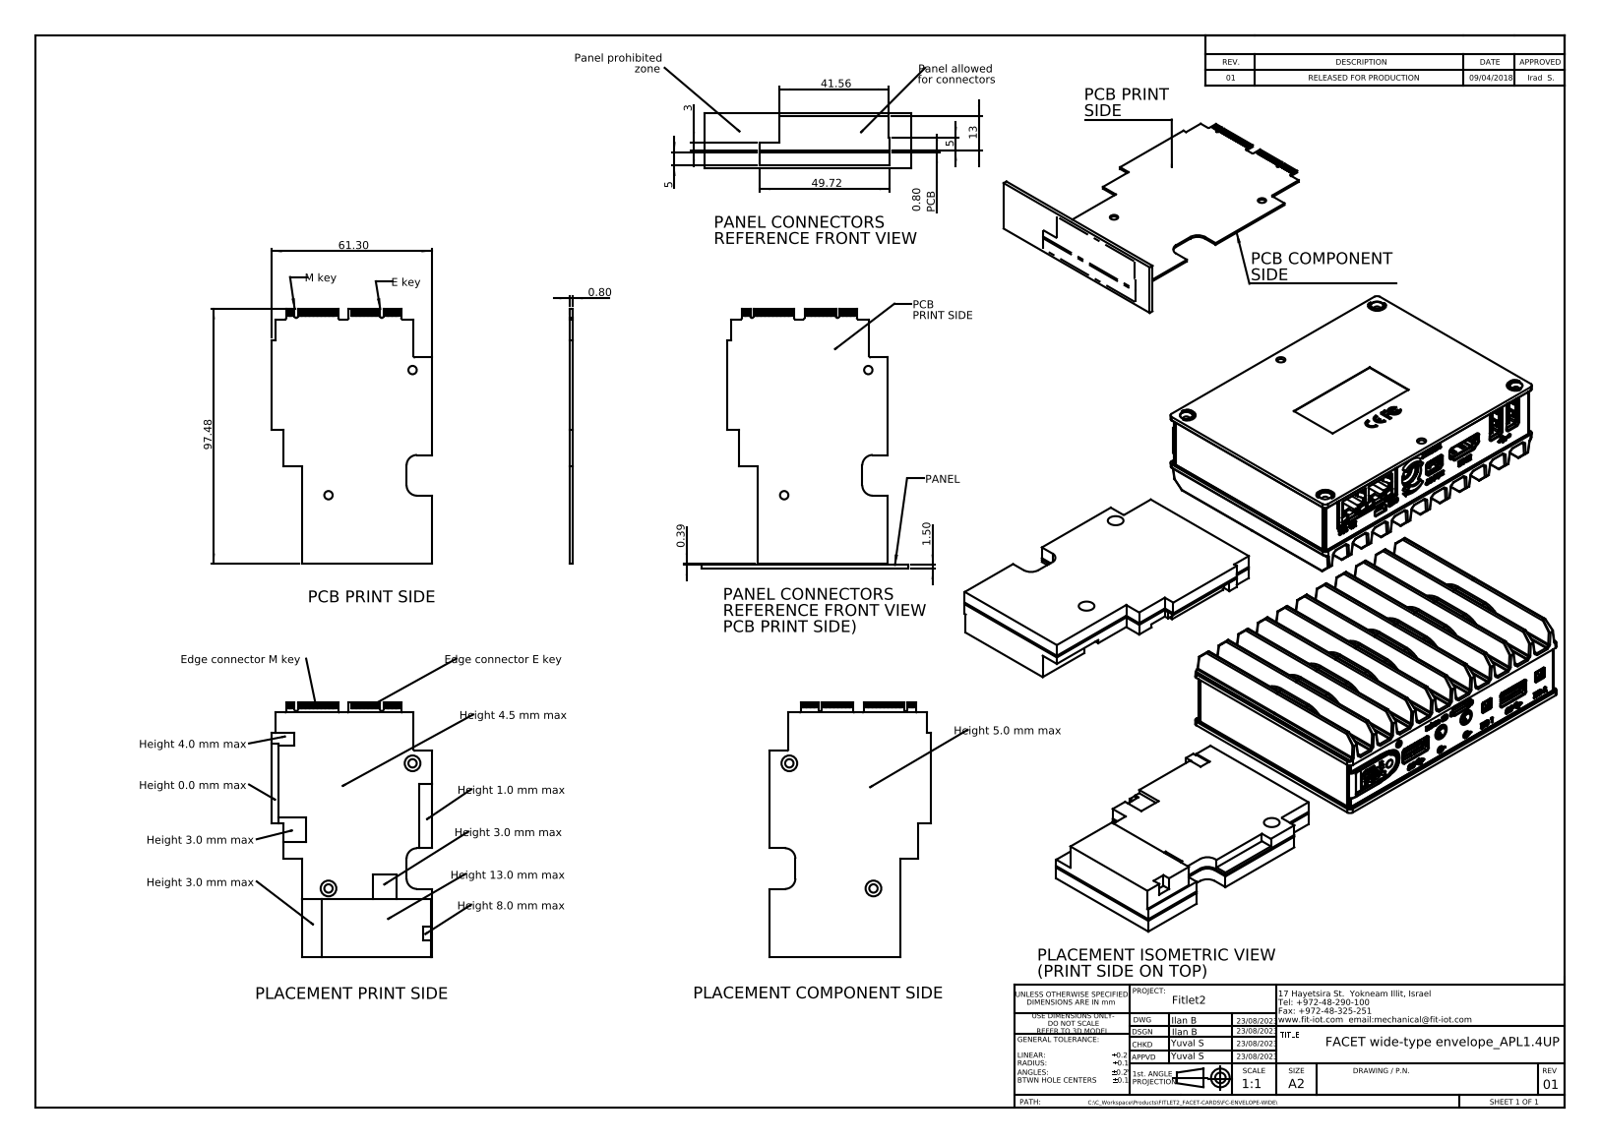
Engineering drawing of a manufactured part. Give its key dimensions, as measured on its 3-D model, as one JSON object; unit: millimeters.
{"part_name": "FACET wide-type envelope_APL1.4UP", "step_written_by": "SolidWorks 2019 (AUTOMOTIVE_DESIGN)", "units": "millimeters", "bodies": {"solids": 137, "faces": 926, "planar": 899, "cylindrical": 27, "other": 0}, "overall_size": [97.48, 61.3, 18.8], "volume_mm3": 57311, "surface_area_mm2": 34837, "round_holes": [[3.2, 2], [6, 2]], "partial_cylinders_radius": [[0.5, 5], [0.6, 2], [4, 2]], "face_to_face_distances": [0.8, 5, 5.8, 10.3, 5.3, 4.5, 13.8, 18.8, 13, 8.5], "hole_center_spacings": [57.61]}
